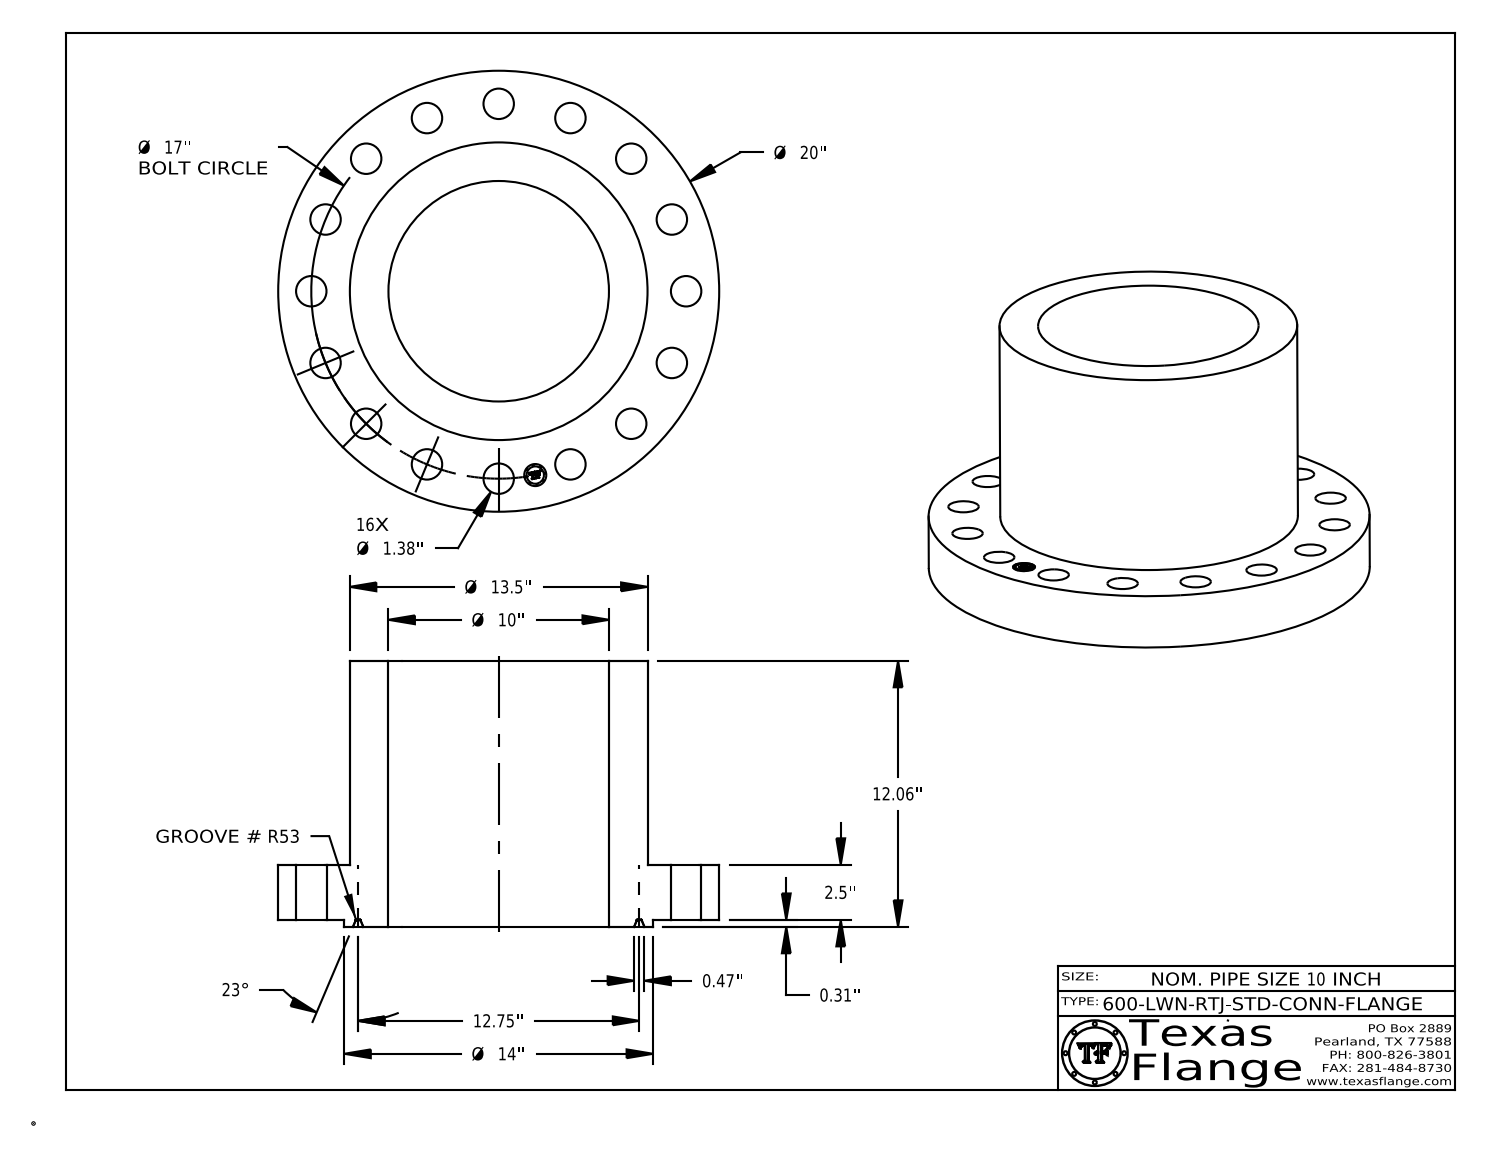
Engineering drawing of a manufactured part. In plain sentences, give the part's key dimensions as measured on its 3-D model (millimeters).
The part is named "10-600-LWN-RTJ-STD-CONN-FLANGE". Its 3-D file was written by "CATIA V5 STEP AP214 (AUTOMOTIVE_DESIGN)". It is 1 solid with 439 faces: 371 planar, 60 cylindrical and 8 other. Overall it measures 508 by 508 by 306.4 millimeters. Its volume is 18 780 000 cubic millimeters and its surface area 1 003 000 square millimeters. Round holes: 16 of diameter 35.1, 1 of diameter 25.4, 1 of diameter 254. Round bosses or shafts: 8 of diameter 1.5, 1 of diameter 508, 1 of diameter 355.6, 1 of diameter 342.9, 1 of diameter 20. The main face-to-face distances are 63.5, 298.5, 235, 8, 71.5, 306.4, 71.3, 63.4, 235.1, 7.6. The hole center spacings are 84.3, 359, 215.9, 165.3, 305.3, 239.9, 239.9, 398.9.
